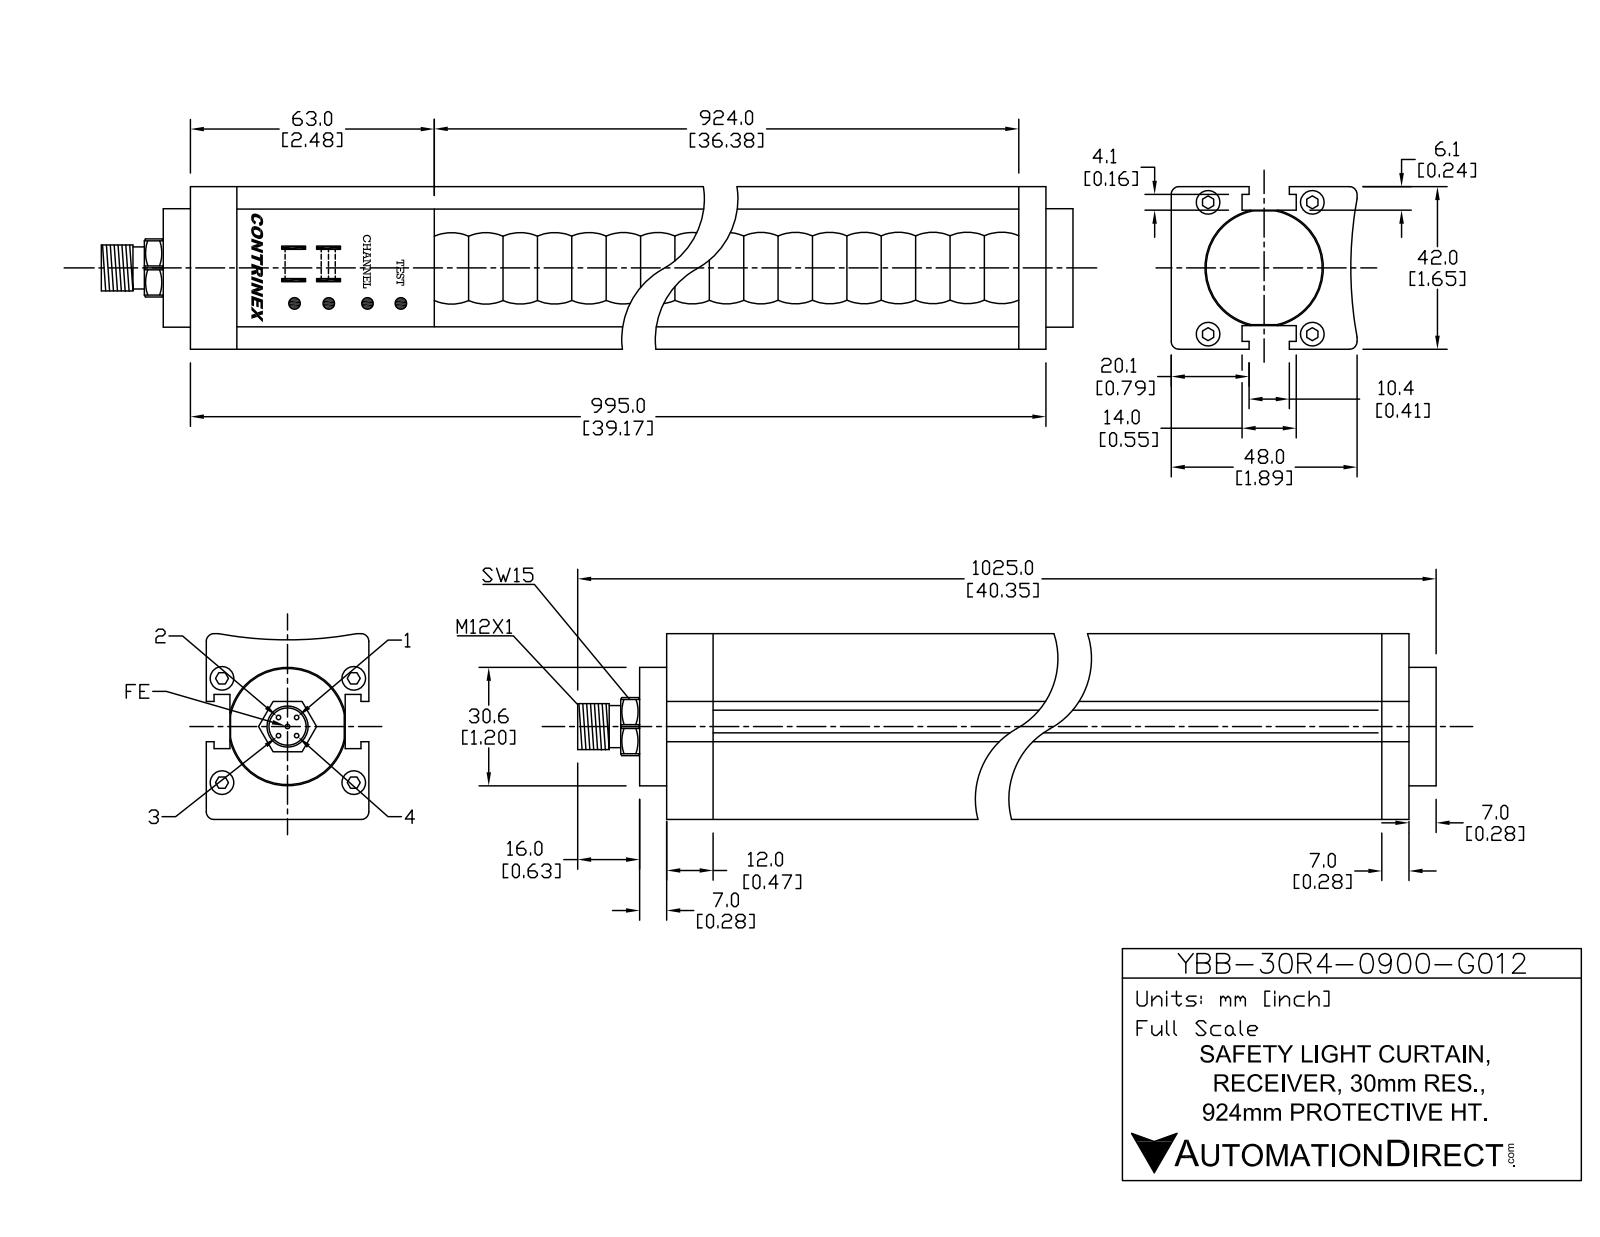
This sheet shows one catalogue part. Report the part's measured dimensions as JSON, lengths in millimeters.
{"part_name": "YBB-30R4-0900-G012", "step_written_by": "SolidWorks 2016 (AUTOMOTIVE_DESIGN)", "units": "millimeters", "bodies": {"solids": 19, "faces": 440, "planar": 208, "cylindrical": 168, "other": 64}, "overall_size": [1025, 48, 42], "volume_mm3": 1792000, "surface_area_mm2": 229874, "round_holes": [[6, 4], [8.5, 1], [32, 1]], "round_bosses_or_shafts": [[1, 5], [5.5, 4], [30.6, 1], [12, 1], [10.5, 1]], "partial_cylinders_radius": [[1, 48], [0.5, 4], [0.55, 2], [8.2, 1], [100, 1]], "face_to_face_distances": [6.3, 35.7, 42, 29.4, 14, 17.2, 31.2, 15.7, 29.7, 46.9], "hole_center_spacings": [21.04, 22.34, 26.9, 34, 43.35]}
